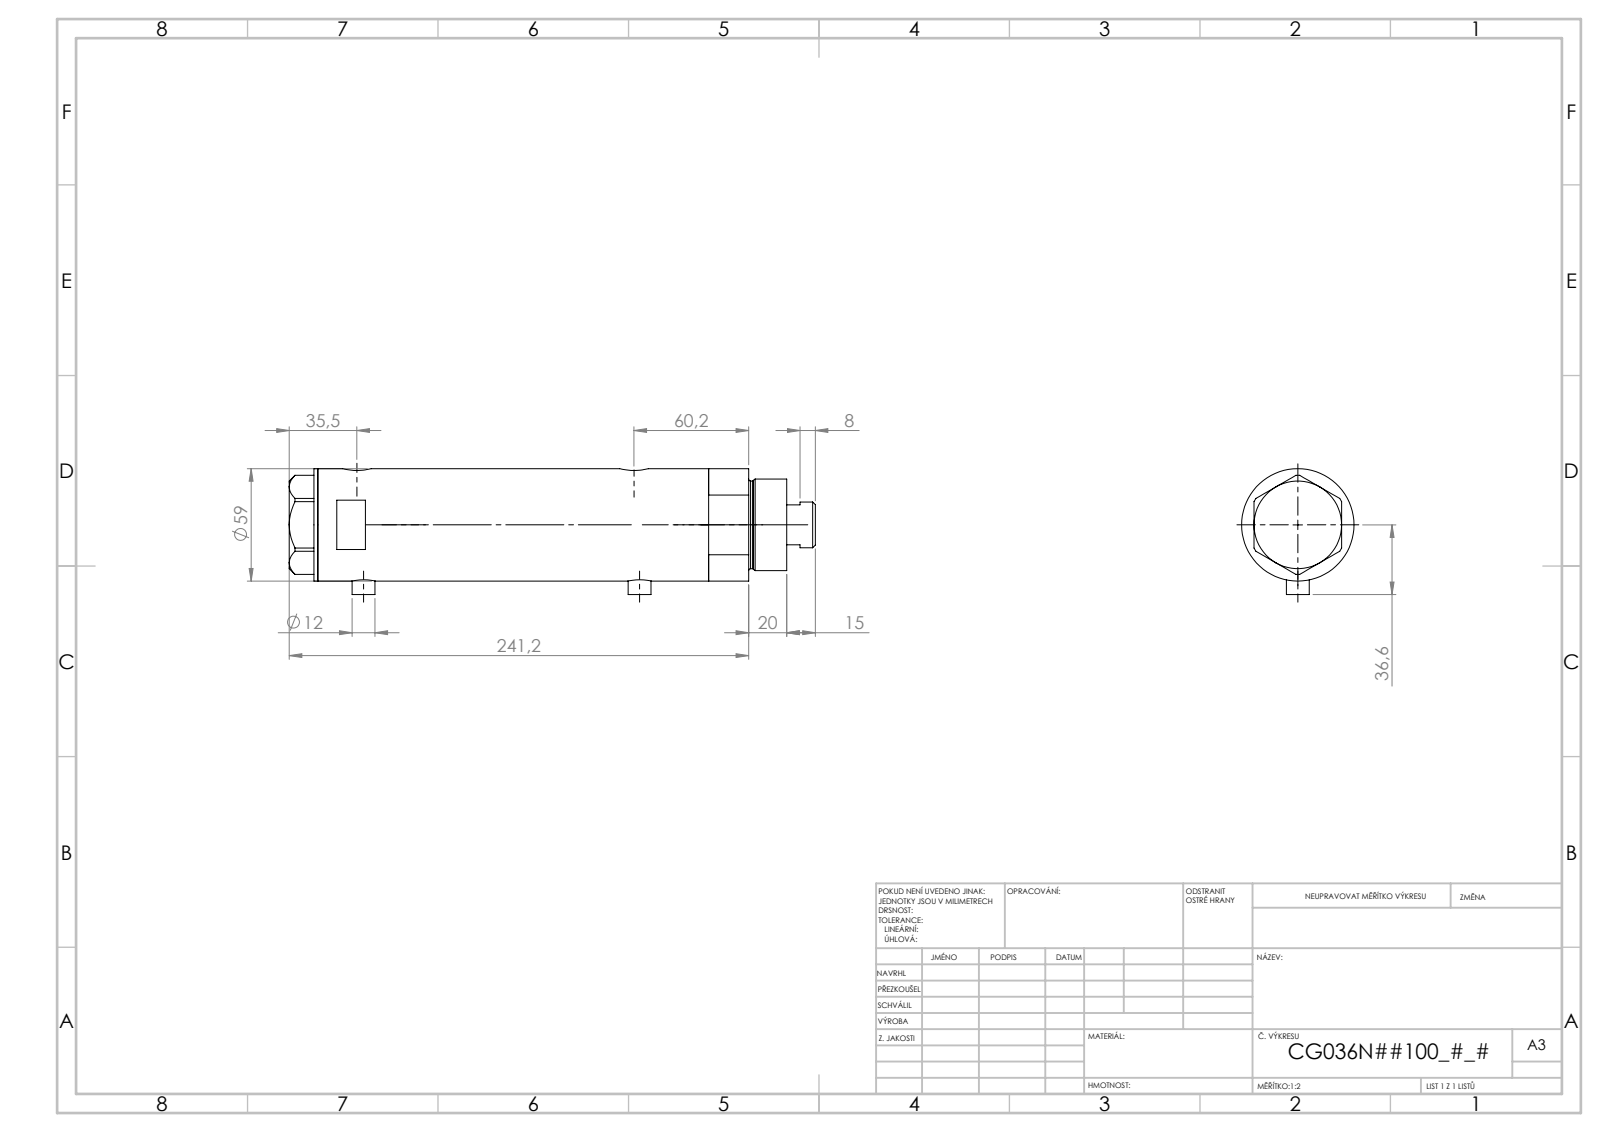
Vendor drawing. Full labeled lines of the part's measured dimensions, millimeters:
Part name (STEP PRODUCT): V270CG_MIDDLE; V270CG_BACK; V270CG_FRONT; V270CG_VC
STEP written by: SolidWorks 2019 (CONFIG_CONTROL_DESIGN)
Units: millimetres
Bodies: 4 solids, 126 faces (53 planar, 53 cylindrical, 20 other)
Overall size (bounding box): 263.42 × 60.1 × 59
Volume: 591 838 mm³ · Surface area: 119 592 mm²
Round holes (diameter × count): ⌀5 ×2, ⌀9.73 ×2, ⌀12.5 ×2, ⌀15 ×2, ⌀8.5 ×1, ⌀25 ×1, ⌀26.5 ×1, ⌀36 ×1, ⌀40 ×1, ⌀52 ×1
Round bosses / shafts (diameter × count): ⌀12 ×2, ⌀59 ×1, ⌀48 ×1, ⌀46 ×1, ⌀24 ×1
Main face-to-face distances: 157.34, 23.5, 133.84, 15, 38.5, 172.34, 248.42, 233.42, 209.92, 76.08
Hole centre spacings: 2.9, 3.5, 132.15, 135.05, 135.65, 138.55, 2.89, 2.91
